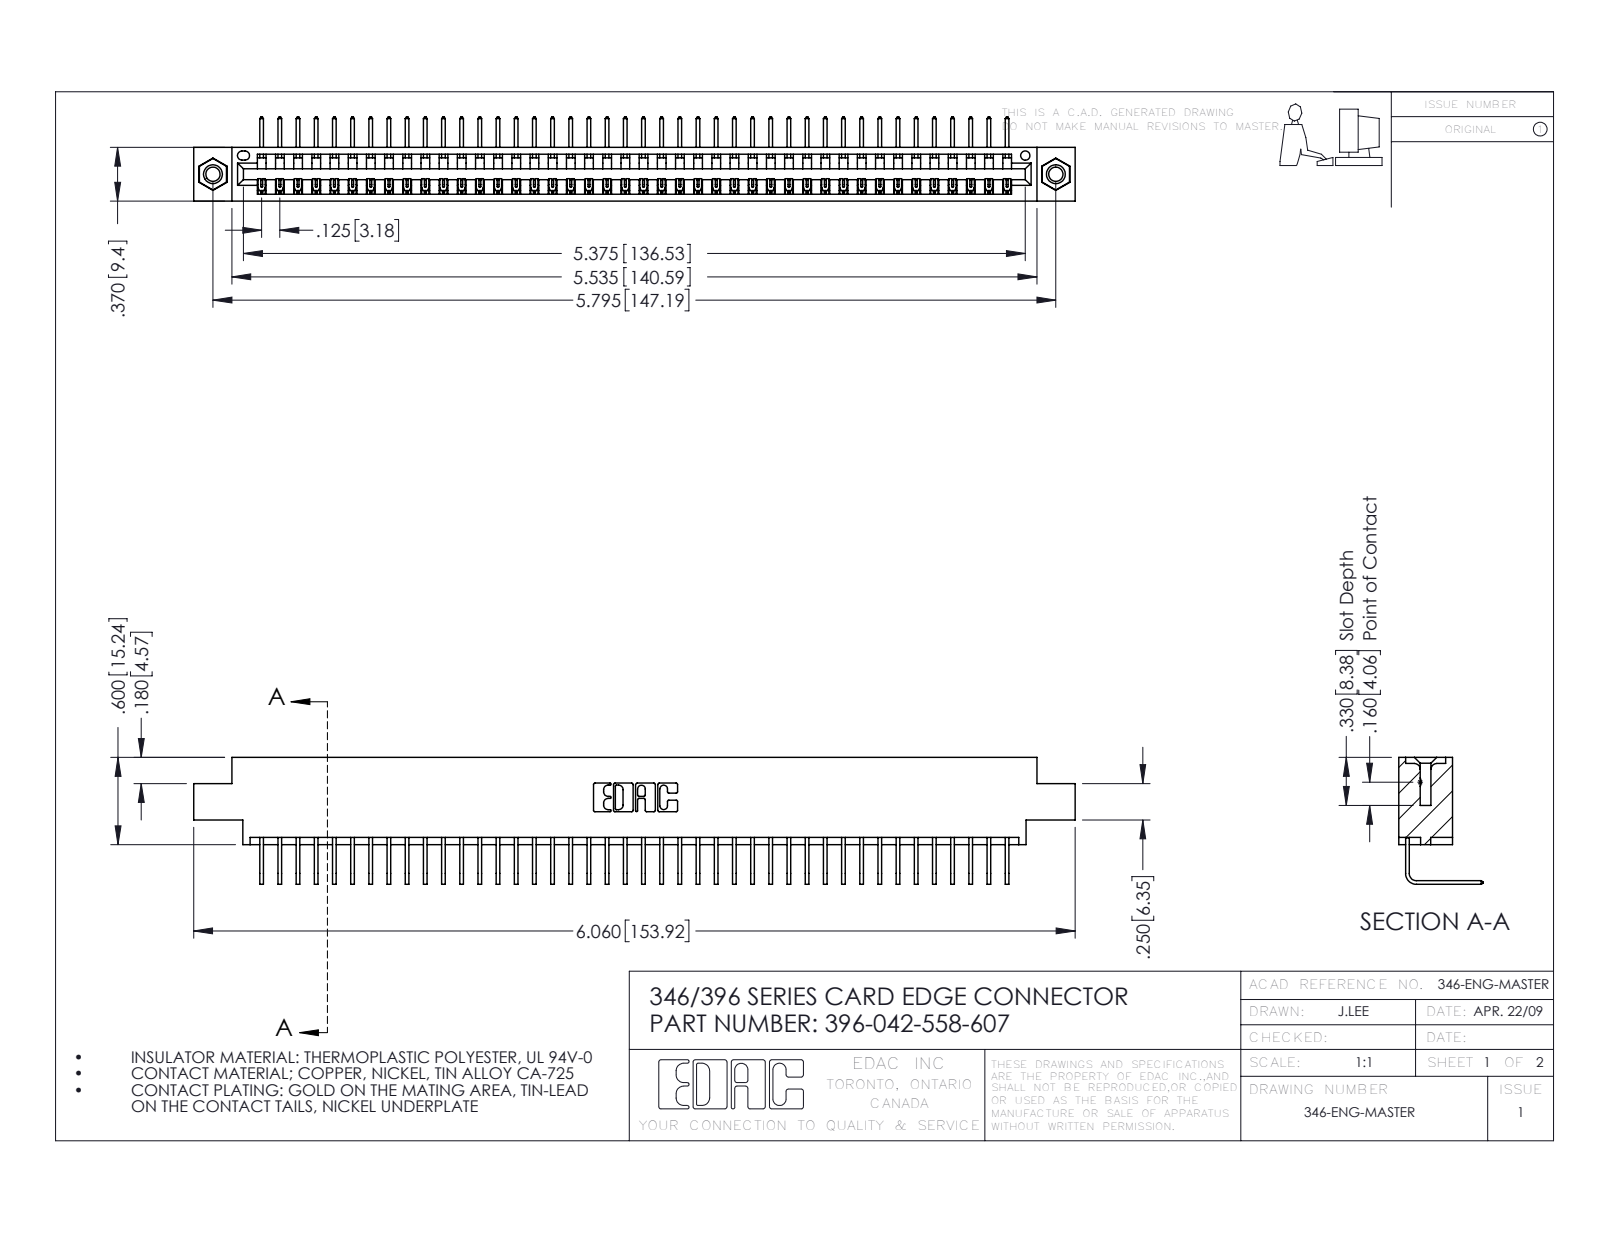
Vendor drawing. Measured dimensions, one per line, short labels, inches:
name: 396-042-558-607; 346 Part_0.170 Offset - 0.156 Dia-TI; 345-292-001_558 Tail - 2; 345-250-001_345-250-005-103
written by: SolidWorks 2016 (CONFIG_CONTROL_DESIGN)
unit: in
bodies: 45 solids, 2706 faces (1876 planar, 814 cylindrical, 16 other)
size: 6.06 × 0.873 × 0.58
volume: 0.897 in³; area: 30.09 in²
holes: 2× ⌀0.098, 2× ⌀0.125, 2× ⌀0.156, 1× ⌀0.064
bosses: 2× ⌀0.155
rounds: 84× R0.006, 22× R0.01, 6× R0.007, 6× R0.031, 3× R0.026, 2× R0.031, 2× R0.04, 1× R0.014
face distances: 0.322, 0.048, 0.37, 0.25, 0.298, 0.025, 0.072, 0.222, 0.148, 0.1
hole spacings: 0.246, 5.586, 5.795
